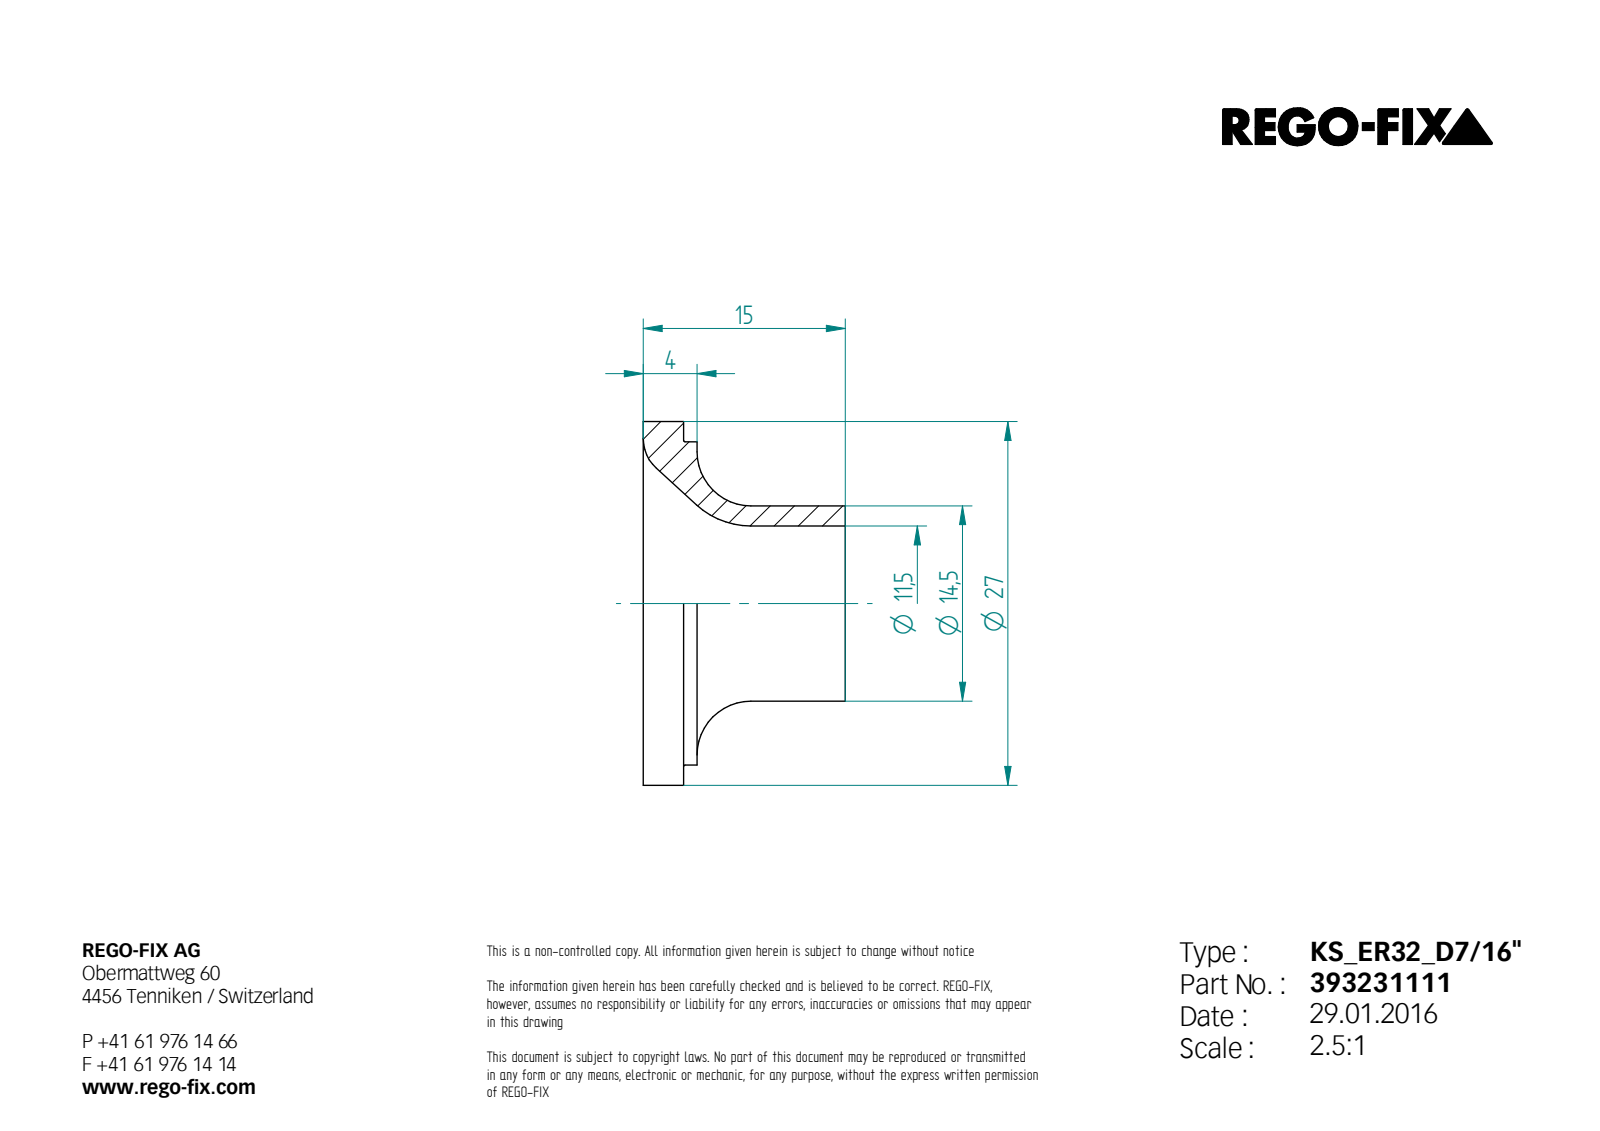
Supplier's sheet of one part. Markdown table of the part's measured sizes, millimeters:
| quantity | value |
| --- | --- |
| STEP written by | Unknown (AUTOMOTIVE_DESIGN) |
| units | millimeters |
| bodies | 1 solid, 13 faces (4 planar, 4 cylindrical, 5 other) |
| overall size | 27 × 27 × 15 |
| volume | 1 874 mm³ |
| surface area | 2 148 mm² |
| round holes (diameter × count) | 11.5 × 1 |
| round bosses / shafts (diameter × count) | 27 × 1, 24 × 1, 14.5 × 1 |
| main face-to-face distances | 3, 15, 12, 4, 1, 11 |
